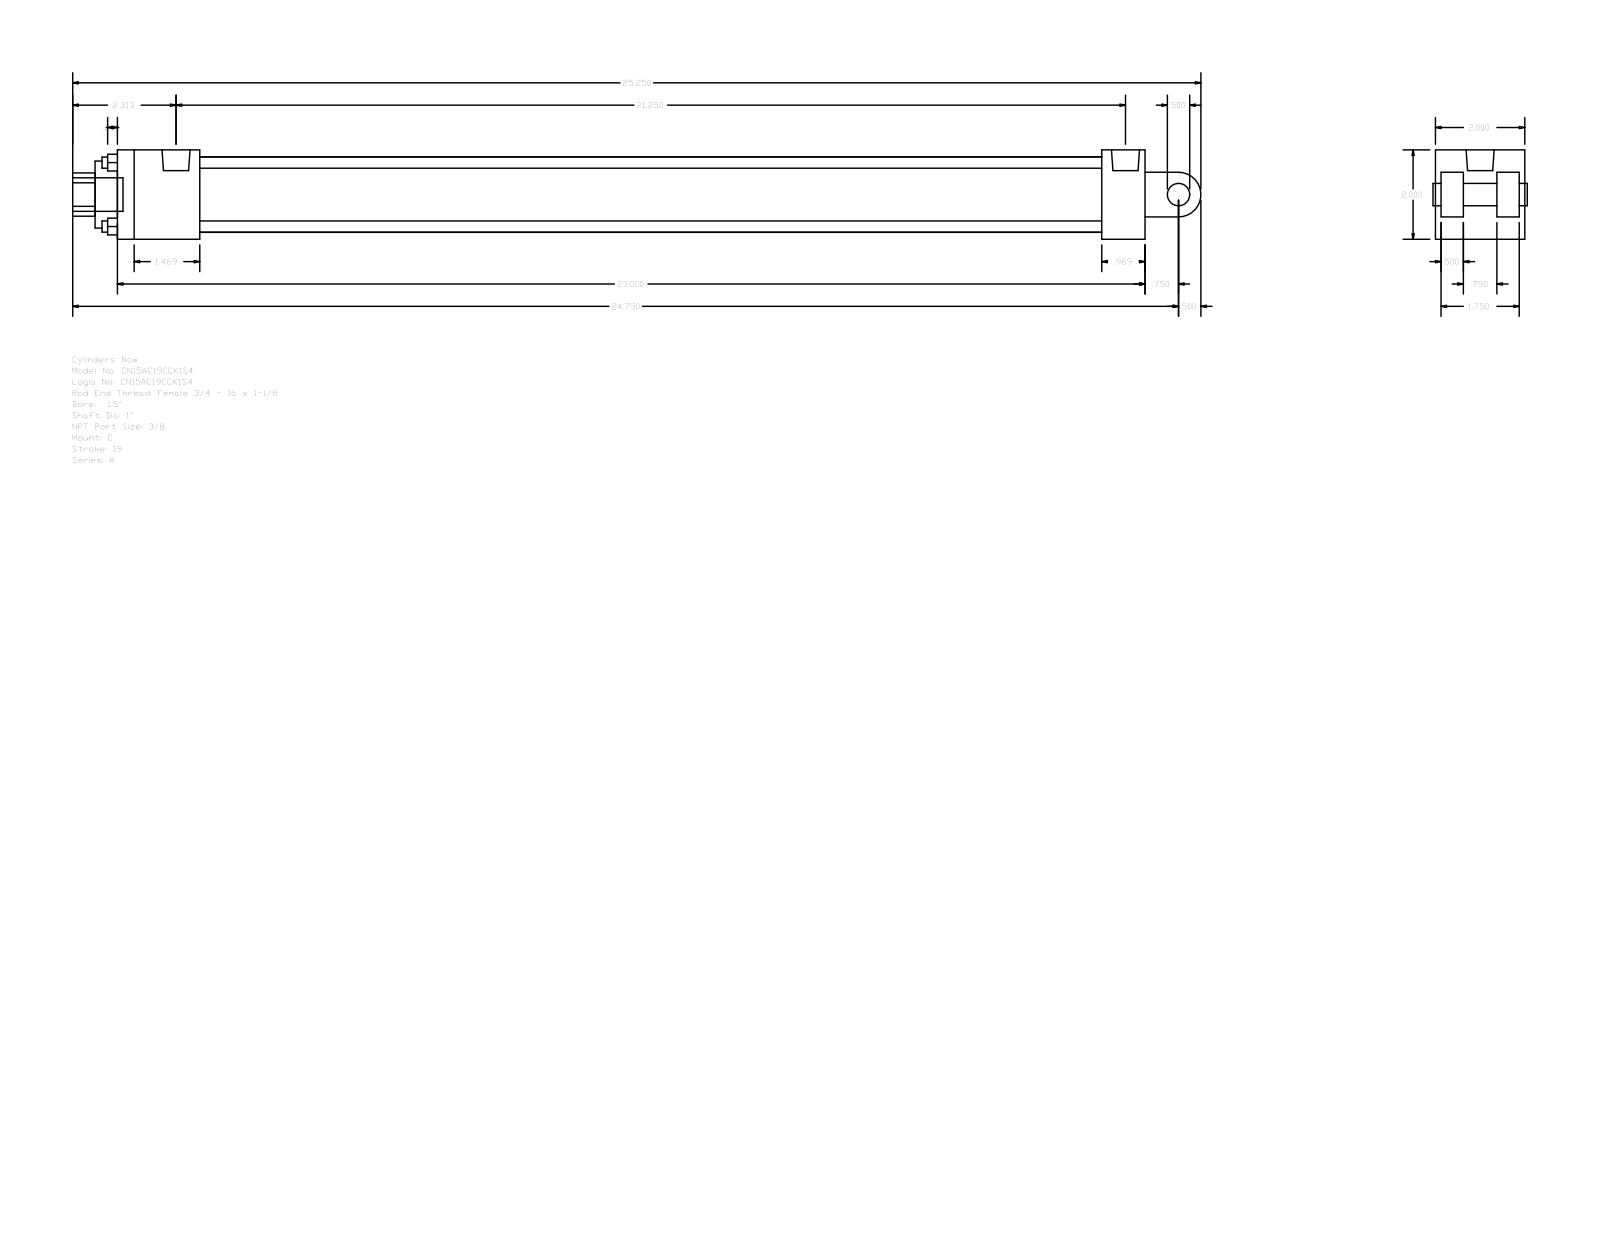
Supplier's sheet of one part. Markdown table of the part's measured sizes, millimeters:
| quantity | value |
| --- | --- |
| part name | A_C__0150_1 |
| STEP written by | GSSL Pune (CONFIG_CONTROL_DESIGN) |
| units | millimeters |
| bodies | 0 solids, 99 faces (70 planar, 29 cylindrical, 0 other) |
| overall size | 641.35 × 50.8 × 50.8 |
| round holes (diameter × count) | 6.35 × 4, 5.56 × 2, 15.93 × 1, 25.4 × 1, 38.1 × 1, 42.93 × 1 |
| round bosses / shafts (diameter × count) | 5.56 × 2, 19.05 × 1, 15.93 × 1, 12.7 × 1 |
| partial cylindrical surfaces (radius × count) | 12.29 × 1, 12.7 × 1 |
| main face-to-face distances | 50.8, 12.7, 3.17, 15.87, 47.63, 34.93, 31.76, 584.2, 559.59, 24.61 |
| hole center spacings | 25.68, 36.32, 51.36, 3.97 |
